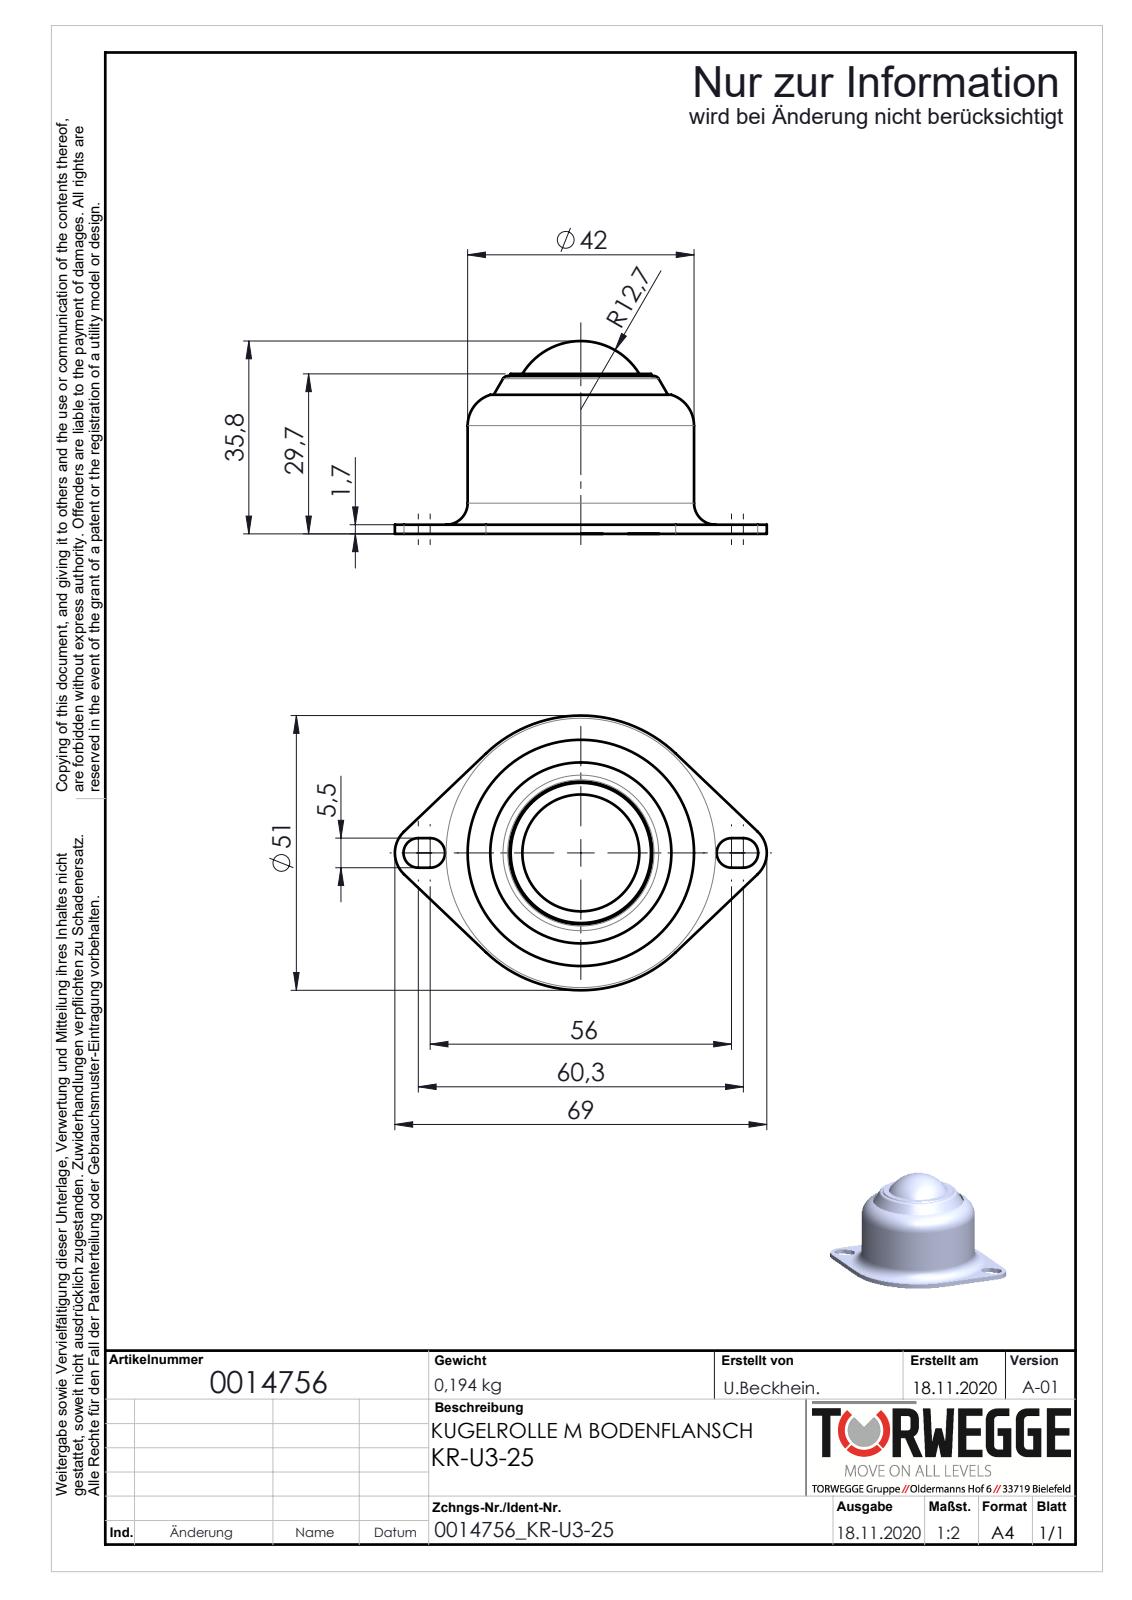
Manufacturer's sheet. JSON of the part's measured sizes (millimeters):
{"part_name": "0014756", "step_written_by": "SolidWorks 2018 (AUTOMOTIVE_DESIGN)", "units": "millimeters", "bodies": {"solids": 1, "faces": 57, "planar": 15, "cylindrical": 21, "other": 21}, "overall_size": [69, 51, 35.8], "volume_mm3": 37601, "surface_area_mm2": 10049, "round_holes": [[2, 1], [8, 1], [20, 1], [33.6, 1]], "round_bosses_or_shafts": [[42, 1], [39.5, 1]], "partial_cylinders_radius": [[2.75, 4], [5.45, 2], [25.5, 1]], "face_to_face_distances": [1.7, 0.91, 0.79, 29.7, 28.79, 28, 51, 29.3, 28.39, 27.6]}
